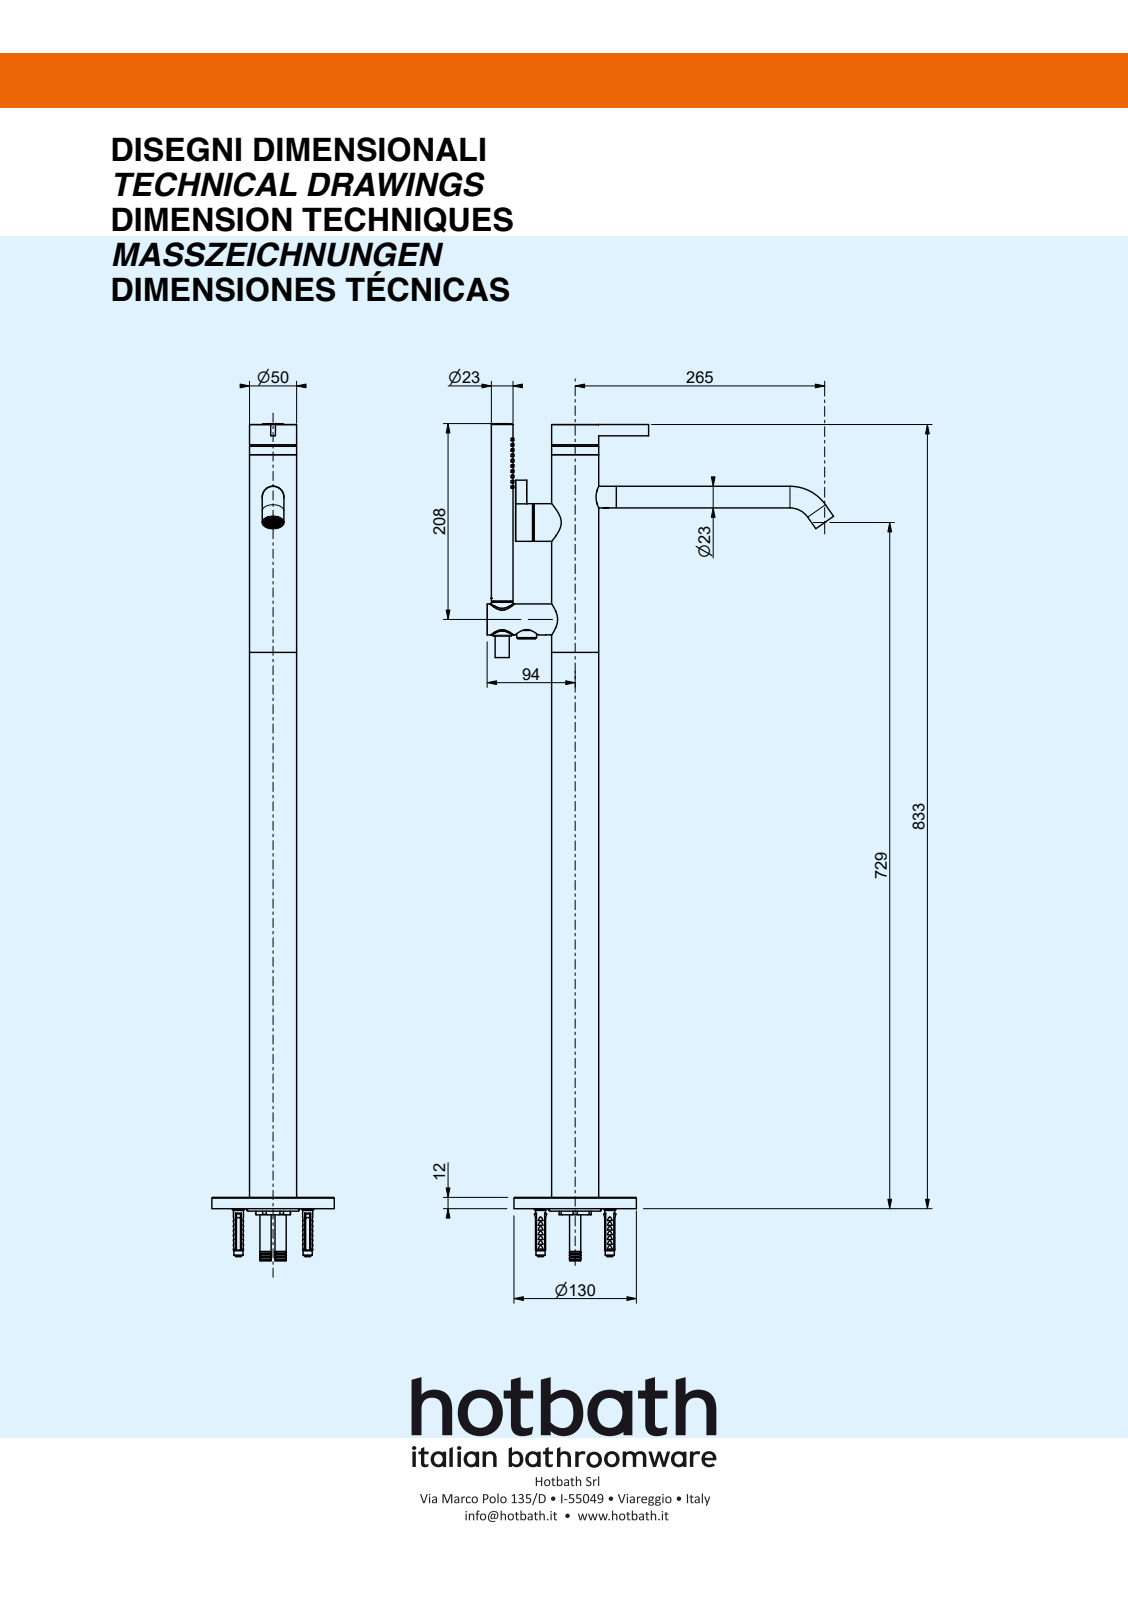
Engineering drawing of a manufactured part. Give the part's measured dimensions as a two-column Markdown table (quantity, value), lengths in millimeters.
| quantity | value |
| --- | --- |
| part name | AF087EXT-00; BSICTXA017_1; AF087-01; AF087-001 (+8 more) |
| STEP written by | Solid Edge (AUTOMOTIVE_DESIGN) |
| units | millimeters |
| bodies | 68 solids, 19658 faces (17709 planar, 898 cylindrical, 1051 other) |
| overall size | 834.1 × 367.88 × 130 |
| volume | 889 991 mm³ |
| surface area | 507 110 mm² |
| round holes (diameter × count) | 2.7 × 40, 3.2 × 6, 8 × 6, 4.2 × 5, 2.2 × 4, 2.3 × 4, 2.5 × 4, 7 × 3, 9 × 3, 14 × 3, 16.5 × 3, 3 × 2 |
| round bosses / shafts (diameter × count) | 5 × 5, 3 × 5, 23 × 4, 12 × 4, 11 × 4, 10 × 4, 6 × 4, 4.3 × 4 |
| partial cylindrical surfaces (radius × count) | 0.5 × 143, 1 × 42, 0.2 × 16, 0.1 × 14, 0.8 × 12, 1.4 × 12, 2 × 10, 0.3 × 8 |
| main face-to-face distances | 3.5, 5, 1.5, 4.6, 12, 10.5, 7, 818, 826.1, 822.6 |
| hole center spacings | 5.6, 6.66, 11.2, 11.76, 16.8, 17.18, 22.4, 22.69 |
